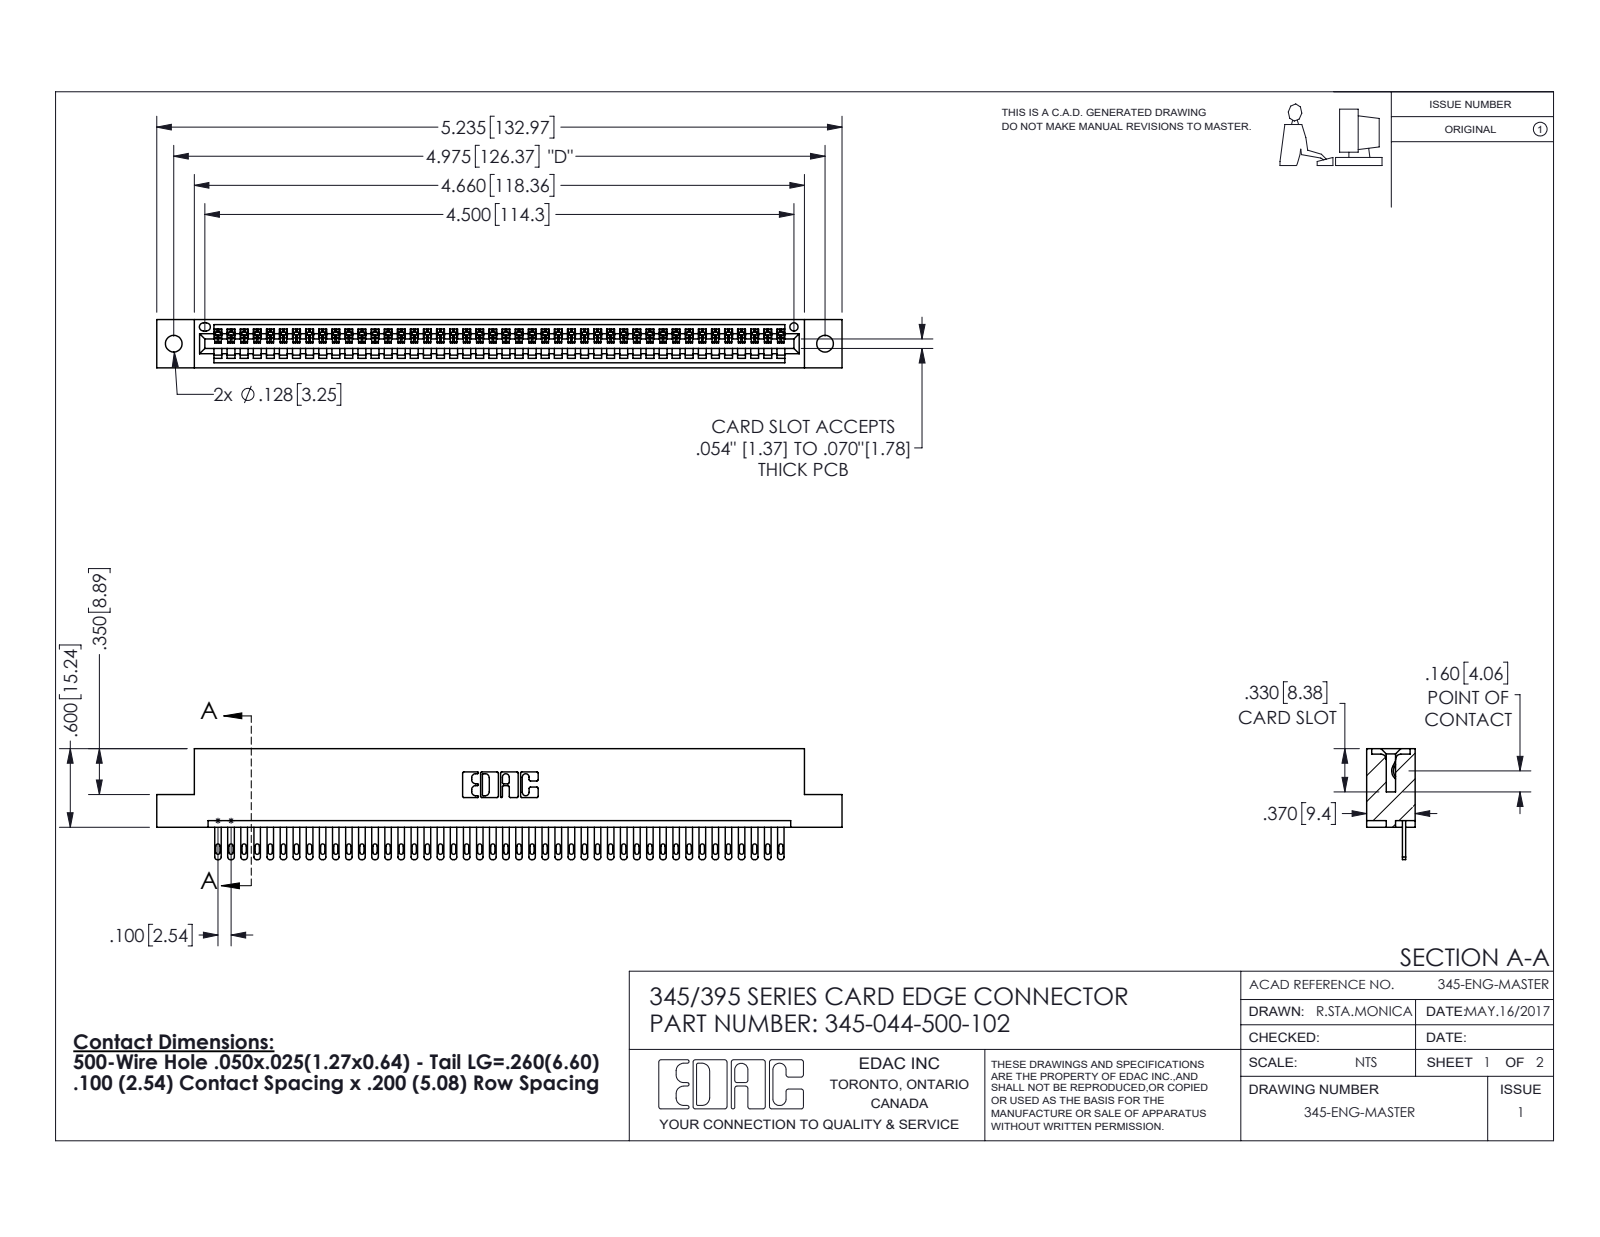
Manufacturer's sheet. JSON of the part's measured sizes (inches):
{"part_name": "345-044-500-102; 345-292-001_345-293-100; 345 Part_Flush Mounting Lugs - 0.128 Dia", "step_written_by": "SolidWorks 2016 (CONFIG_CONTROL_DESIGN)", "units": "inches", "bodies": {"solids": 45, "faces": 2502, "planar": 1576, "cylindrical": 926, "other": 0}, "overall_size": [5.235, 0.847, 0.37], "volume_in3": 0.771, "surface_area_in2": 25.8, "round_holes": [[0.128, 2], [0.064, 1]], "partial_cylinders_radius": [[0.006, 88], [0.016, 88], [0.02, 88], [0.01, 22], [0.007, 6], [0.031, 6], [0.026, 3], [0.031, 2]], "face_to_face_distances": [0.298, 0.072, 0.37, 0.2, 0.098, 0.272, 0.025, 0.225, 0.149, 0.072], "hole_center_spacings": [0.27, 4.739, 4.975]}
